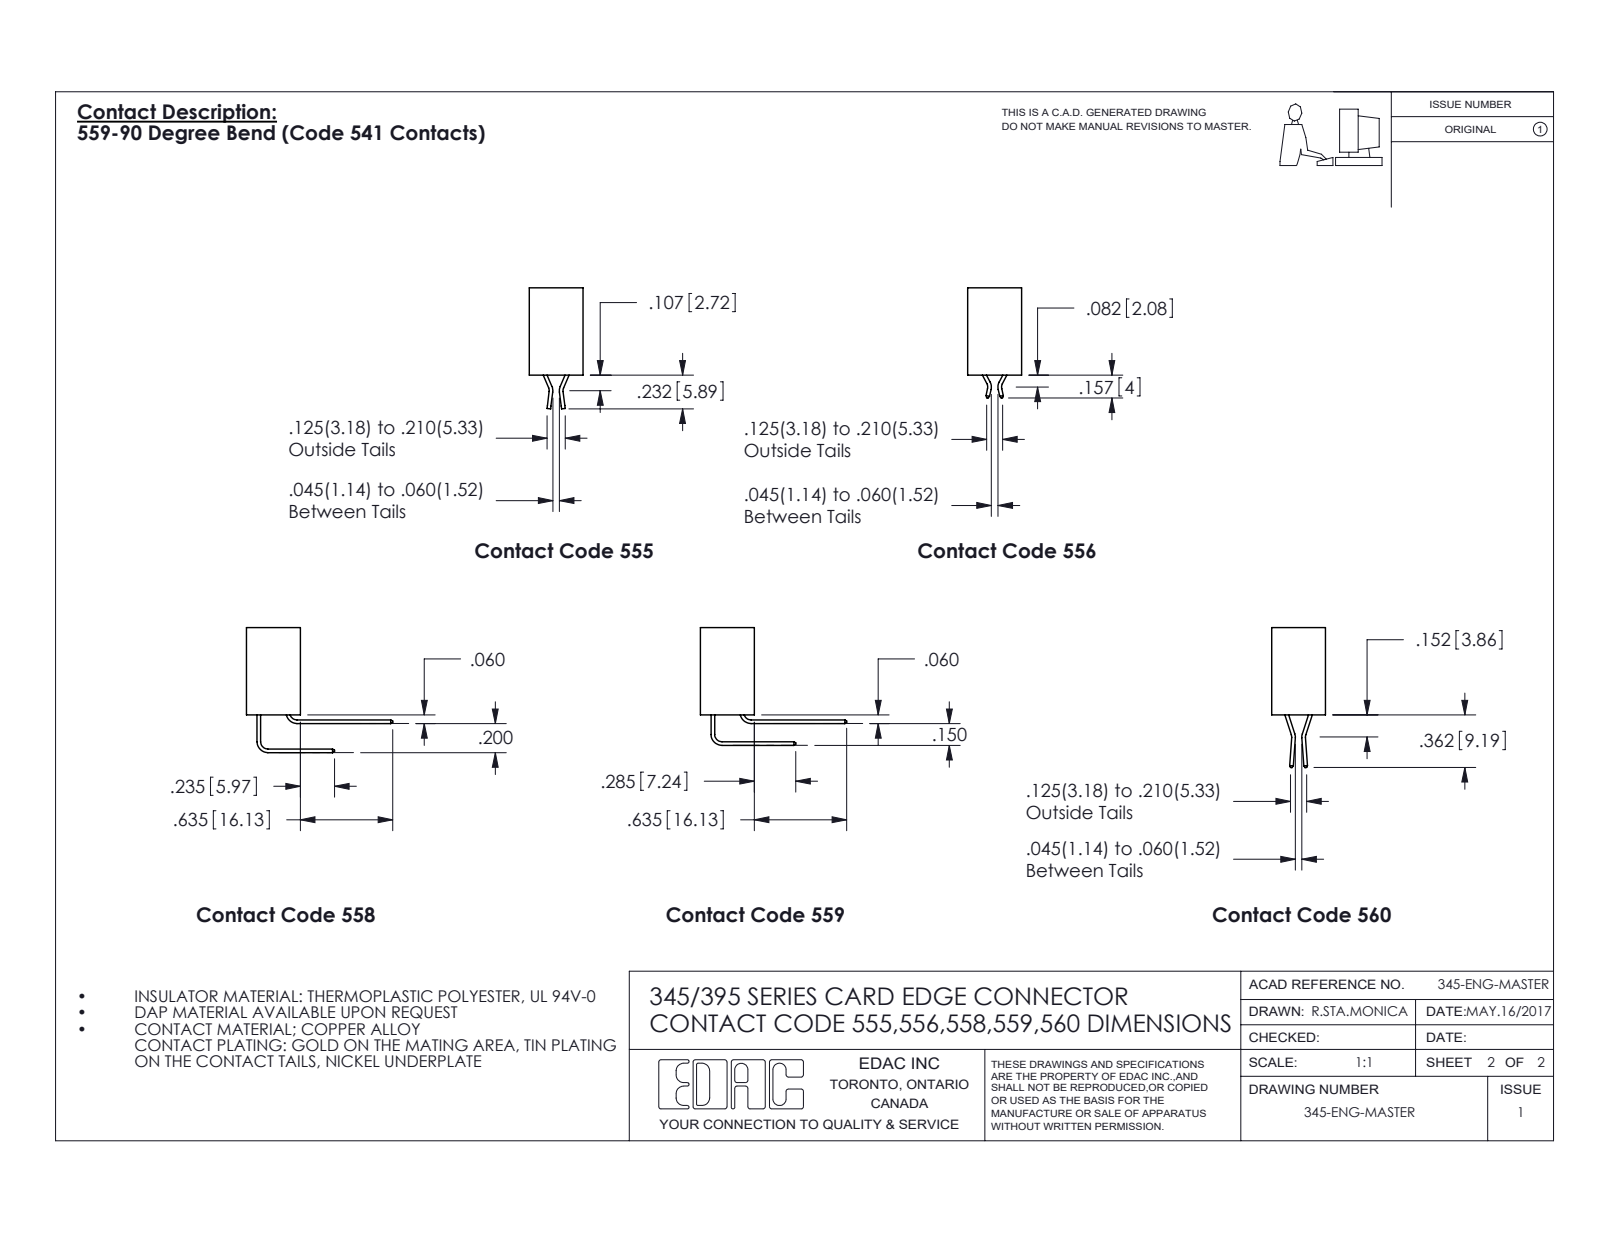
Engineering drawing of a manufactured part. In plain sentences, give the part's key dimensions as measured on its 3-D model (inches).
The part is named "345-005-559-101; 345-292-001_558 559 Tail - 1; 345 Part_No Mounting Lugs". Its 3-D file was written by "SolidWorks 2016 (CONFIG_CONTROL_DESIGN)". It is 6 solids with 418 faces: 286 planar, 132 cylindrical and 0 other. Overall it measures 1.005 by 0.76 by 0.659 inches. Its volume is 0.13 cubic inches and its surface area 4.057 square inches. Round holes: 1 of diameter 0.064. Partial cylindrical surfaces (rounded edges, fillets, slot ends): 22 of radius 0.01, 10 of radius 0.006, 6 of radius 0.007, 6 of radius 0.031, 3 of radius 0.026, 2 of radius 0.031, 2 of radius 0.04, 1 of radius 0.014. The main face-to-face distances are 0.2, 0.1, 0.37, 0.298, 0.072, 0.06, 0.3, 0.76, 0.098, 0.272.
